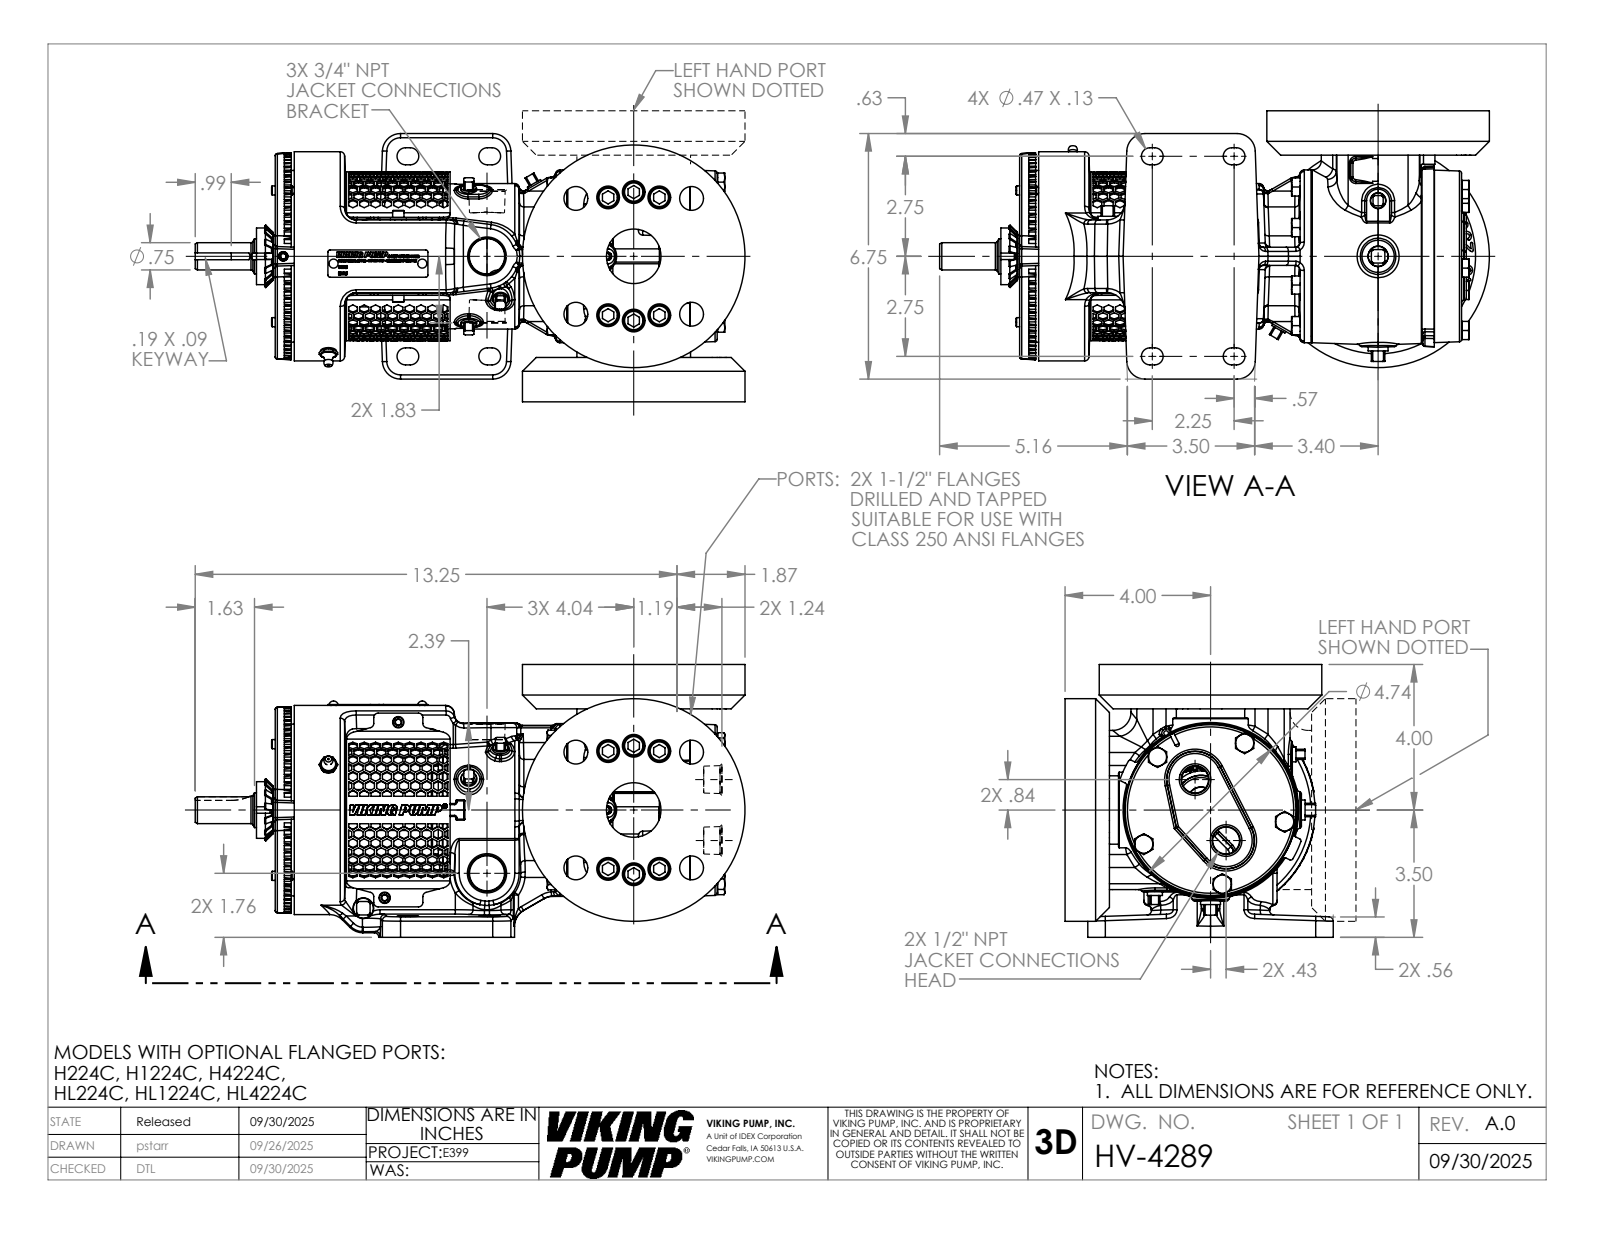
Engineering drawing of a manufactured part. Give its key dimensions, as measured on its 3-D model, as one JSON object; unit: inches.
{"part_name": "HV-4289", "step_written_by": "SolidWorks 2024 (AUTOMOTIVE_DESIGN)", "units": "inches", "bodies": {"solids": 1, "faces": 4372, "planar": 1470, "cylindrical": 877, "other": 2025}, "overall_size": [15.119, 7.5, 7.375], "volume_in3": 270.1, "surface_area_in2": 663.7, "round_holes": [[0.25, 9], [0.625, 8], [0.656, 8], [0.625, 4], [0.159, 3], [0.197, 3], [0.257, 2], [1.5, 2], [0.986, 1], [0.989, 1], [1.265, 1], [4.502, 1]], "round_bosses_or_shafts": [[0.563, 12], [0.5, 5], [0.312, 3], [0.19, 3], [6.12, 2], [0.25, 2], [5.75, 1], [4.75, 1]], "partial_cylinders_radius": [[0.054, 140], [0.12, 81], [0.06, 55], [0.5, 40], [0.03, 22], [0.25, 10], [0.234, 8], [0.422, 8]], "face_to_face_distances": [7.5, 1.22, 1.94, 6.28, 12.154, 10.213, 1.5, 0.524, 1.417, 11.63], "hole_center_spacings": [1.766, 2.56, 0.719, 0.887, 1.6, 2.25, 2.295, 3.182]}
